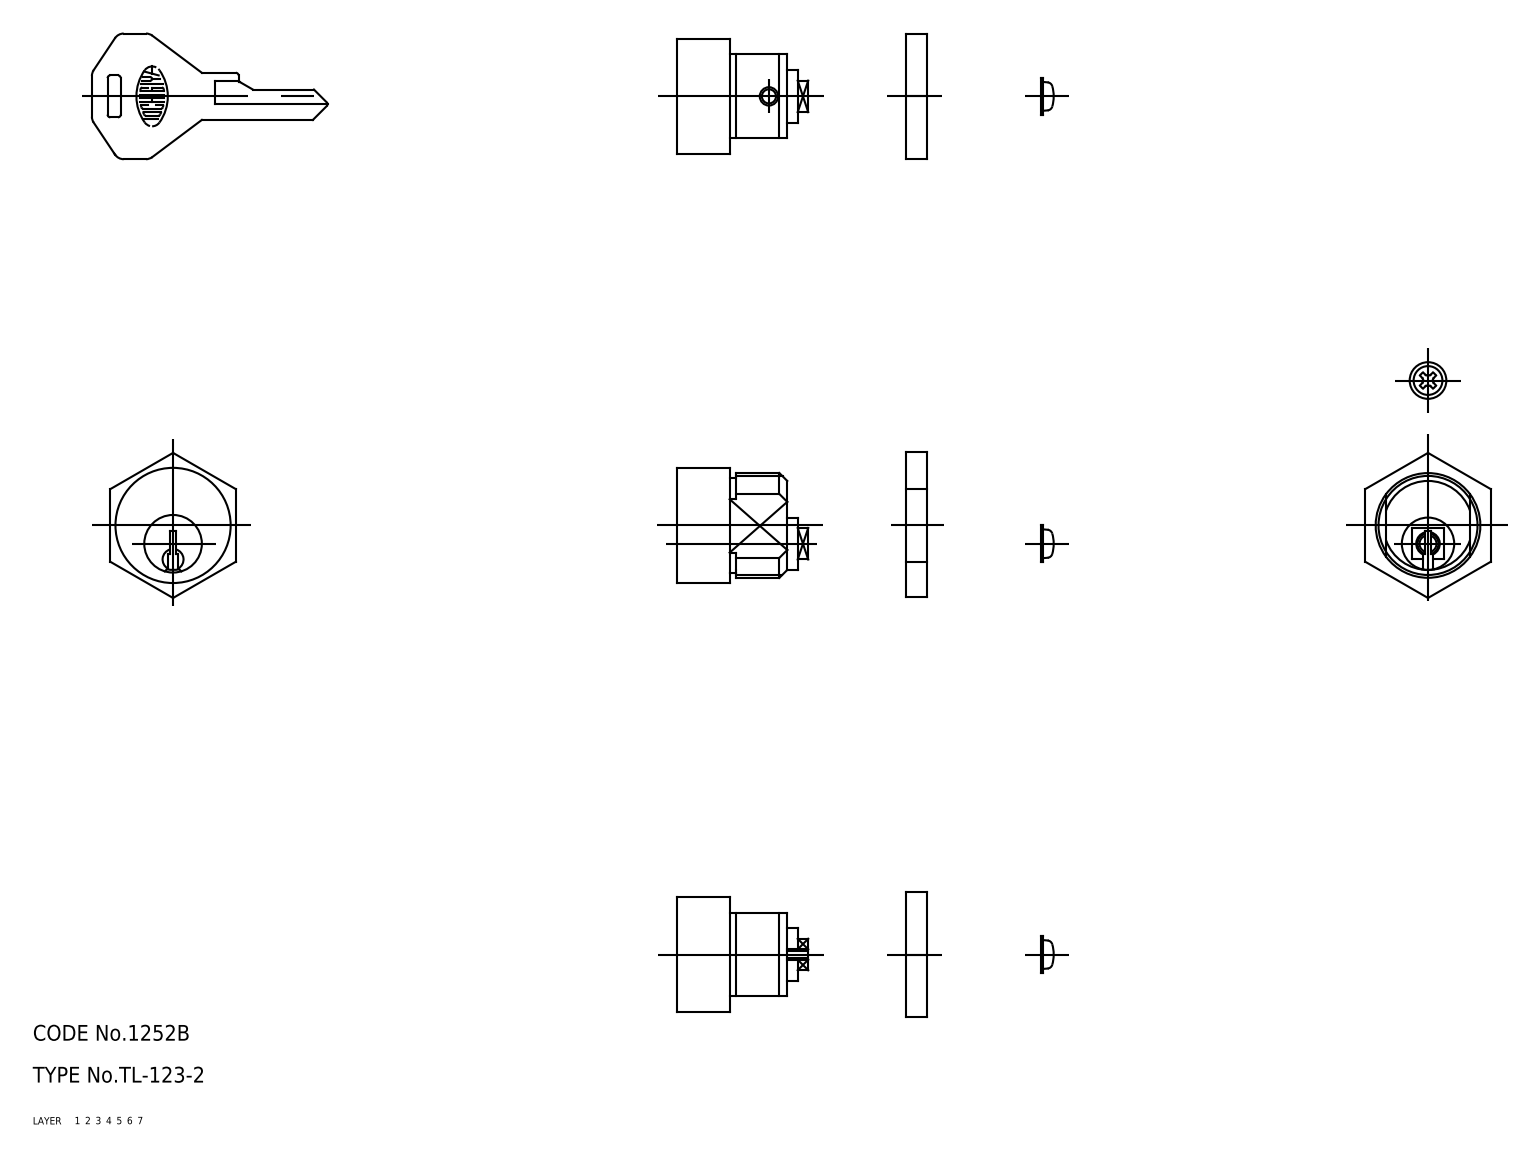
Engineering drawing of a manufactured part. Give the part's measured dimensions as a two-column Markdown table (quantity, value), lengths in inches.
| quantity | value |
| --- | --- |
| part name | 67115011; 67115024; 67115037; 67115050 |
| STEP written by | CADfix (AUTOMOTIVE_DESIGN) |
| units | inches |
| bodies | 4 solids, 134 faces (0 planar, 0 cylindrical, 134 other) |
| overall size | 3.715 × 1.175 × 0.945 |
| volume | 0.513 in³ |
| surface area | 9.449 in² |
